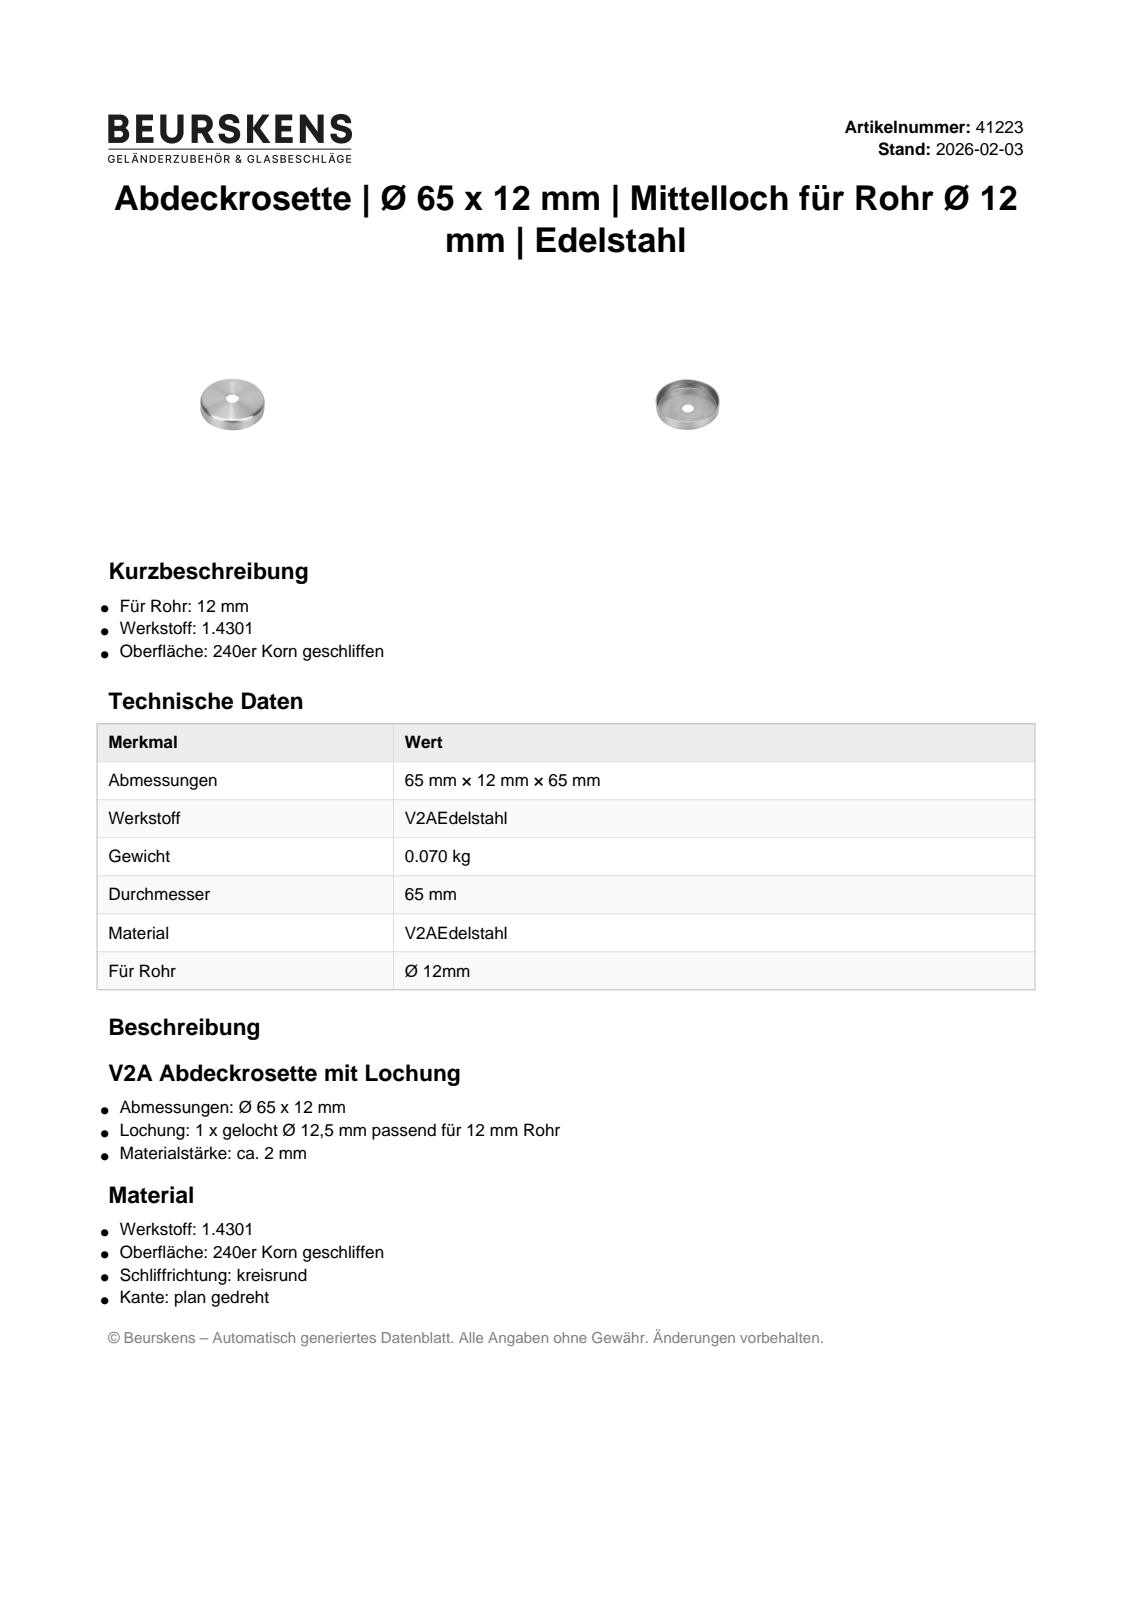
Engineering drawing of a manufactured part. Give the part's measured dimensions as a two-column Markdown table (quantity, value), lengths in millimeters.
| quantity | value |
| --- | --- |
| part name | 41223 |
| STEP written by | Autodesk Inventor 2022 (AUTOMOTIVE_DESIGN) |
| units | millimeters |
| bodies | 1 solid, 8 faces (3 planar, 3 cylindrical, 2 other) |
| overall size | 65 × 65 × 12 |
| volume | 7 642 mm³ |
| surface area | 10 552 mm² |
| round holes (diameter × count) | 12.5 × 1, 62 × 1 |
| round bosses / shafts (diameter × count) | 65 × 1 |
| main face-to-face distances | 1.5, 10.5, 12 |
